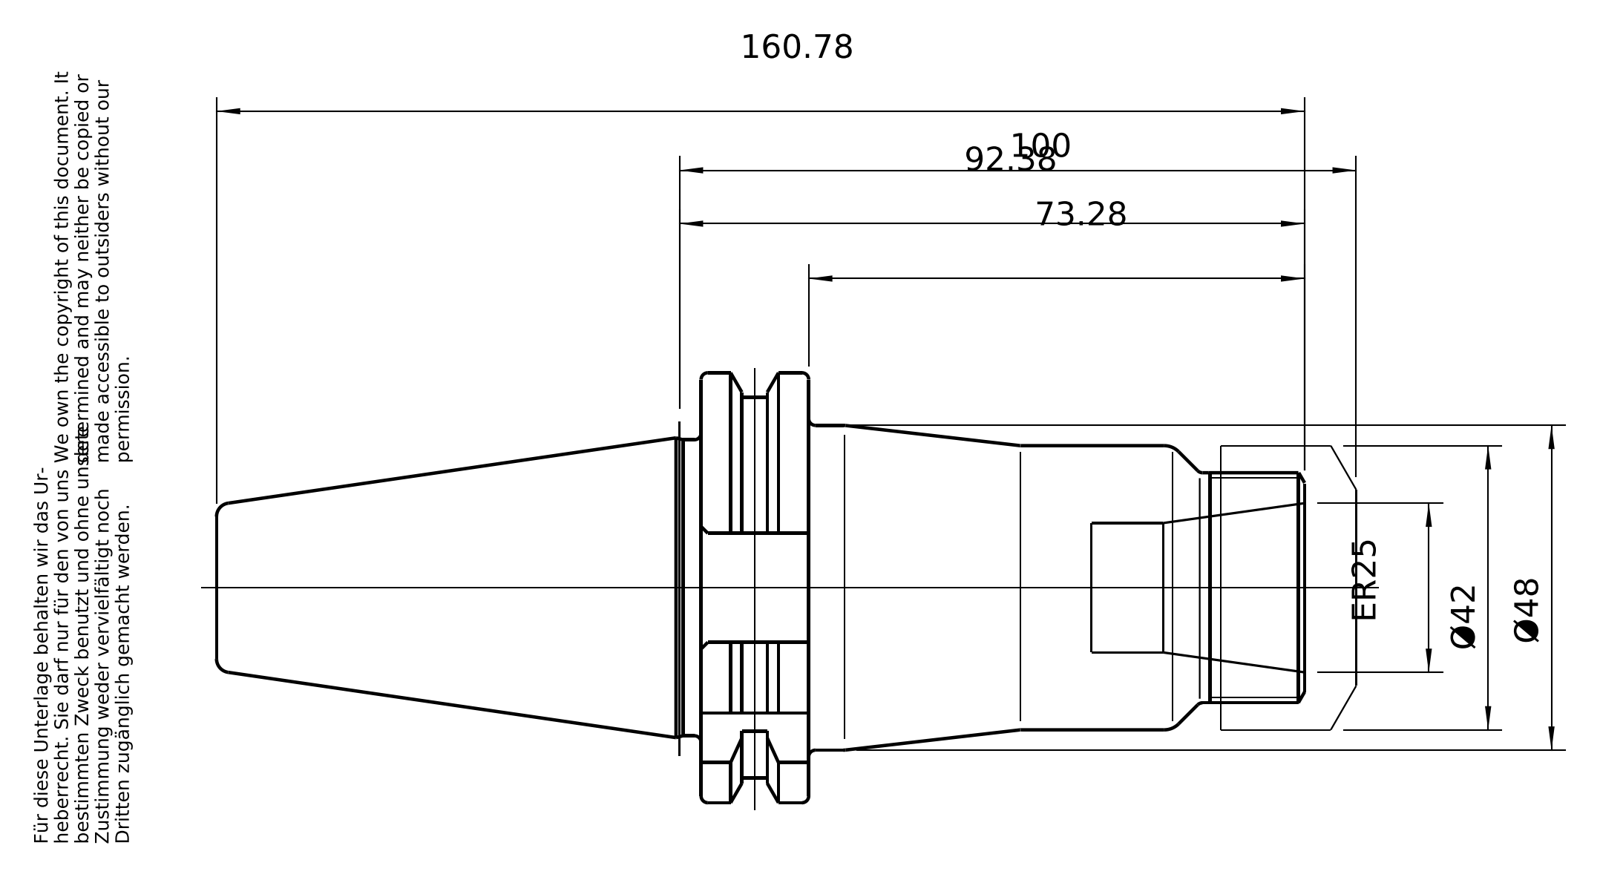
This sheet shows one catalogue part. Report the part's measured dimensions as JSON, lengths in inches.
{"part_name": "40-321-25-3; 83-914-25; 40-321-25-3_ASM", "step_written_by": "PRO/ENGINEER BY PARAMETRIC TECHNOLOGY CORPORATION, 2010430 (CONFIG_CONTROL_DESIGN)", "units": "inches", "bodies": {"solids": 2, "faces": 176, "planar": 31, "cylindrical": 55, "other": 90}, "overall_size": [6.624, 2.501, 2.418], "volume_in3": 12.67, "surface_area_in2": 57.66, "round_holes": [[0.079, 1], [0.545, 1], [0.67, 1], [0.689, 1], [0.753, 1], [0.823, 1], [1.118, 1], [1.26, 1], [1.366, 1]], "round_bosses_or_shafts": [[1.89, 1], [1.722, 1], [1.654, 1], [1.339, 1], [0.63, 1]], "partial_cylinders_radius": [[0.118, 8], [0.197, 2], [0.484, 2], [0.053, 1], [0.251, 1], [0.506, 1], [1.102, 1], [1.25, 1]], "face_to_face_distances": [0.624, 3.811, 3.187, 3.511, 2.887, 0.3, 3.535, 2.911, 0.024, 0.276], "hole_center_spacings": [0.728]}
